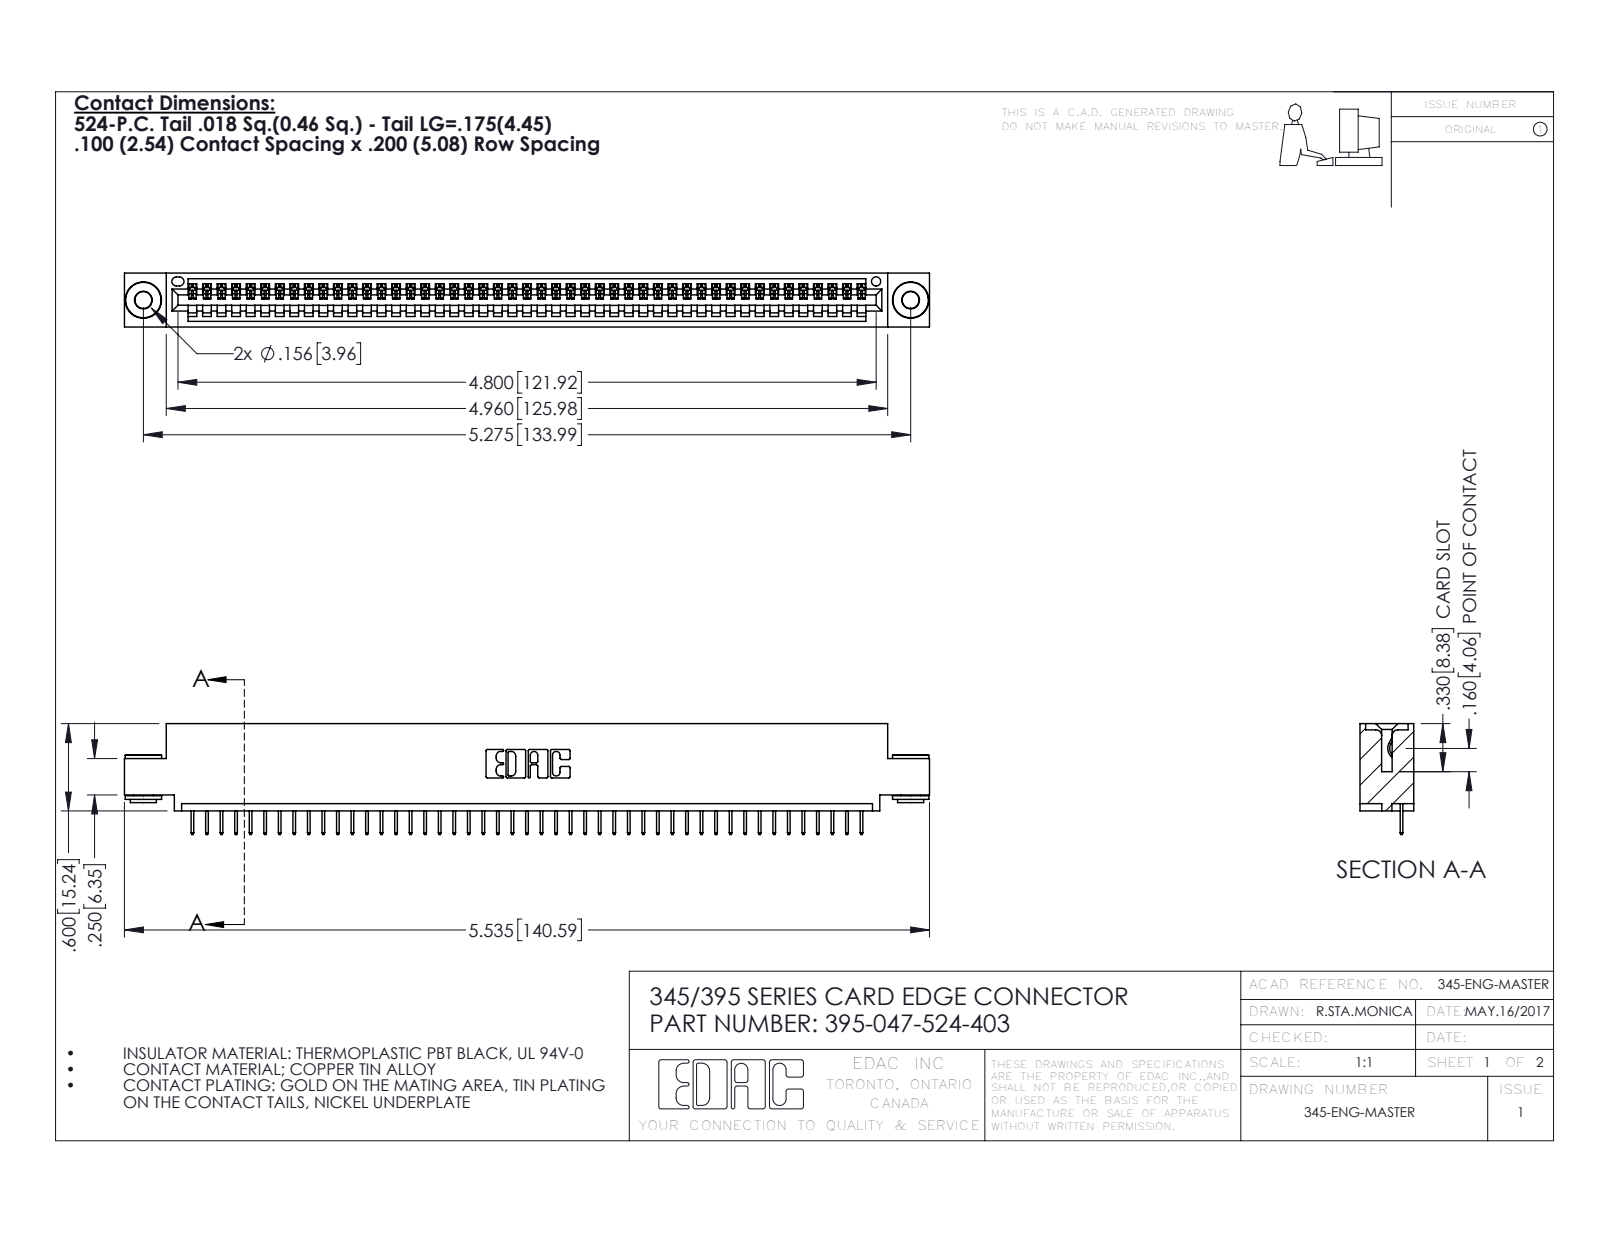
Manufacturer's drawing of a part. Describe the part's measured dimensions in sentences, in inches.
The part is named "395-047-524-403; 345 Part_0.110 Offset - 0.156 Dia-TH; 345-250-002_345-250-002-102; 345-292-001_345-293-124". Its 3-D file was written by "SolidWorks 2016 (CONFIG_CONTROL_DESIGN)". It is 50 solids with 3082 faces: 2256 planar, 818 cylindrical and 8 other. Overall it measures 5.535 by 0.762 by 0.37 inches. Its volume is 0.803 cubic inches and its surface area 26.74 square inches. Round holes: 2 of diameter 0.116, 2 of diameter 0.156, 1 of diameter 0.064. Round bosses or shafts: 2 of diameter 0.25, 2 of diameter 0.18, 2 of diameter 0.136. Partial cylindrical surfaces (rounded edges, fillets, slot ends): 94 of radius 0.006, 22 of radius 0.01, 6 of radius 0.007, 6 of radius 0.031, 3 of radius 0.026, 2 of radius 0.031, 2 of radius 0.04, 1 of radius 0.014. The main face-to-face distances are 0.072, 0.298, 0.37, 0.2, 0.025, 0.098, 0.272, 0.225, 0.072, 0.149. The hole center spacings are 0.27, 5.039, 5.275.
